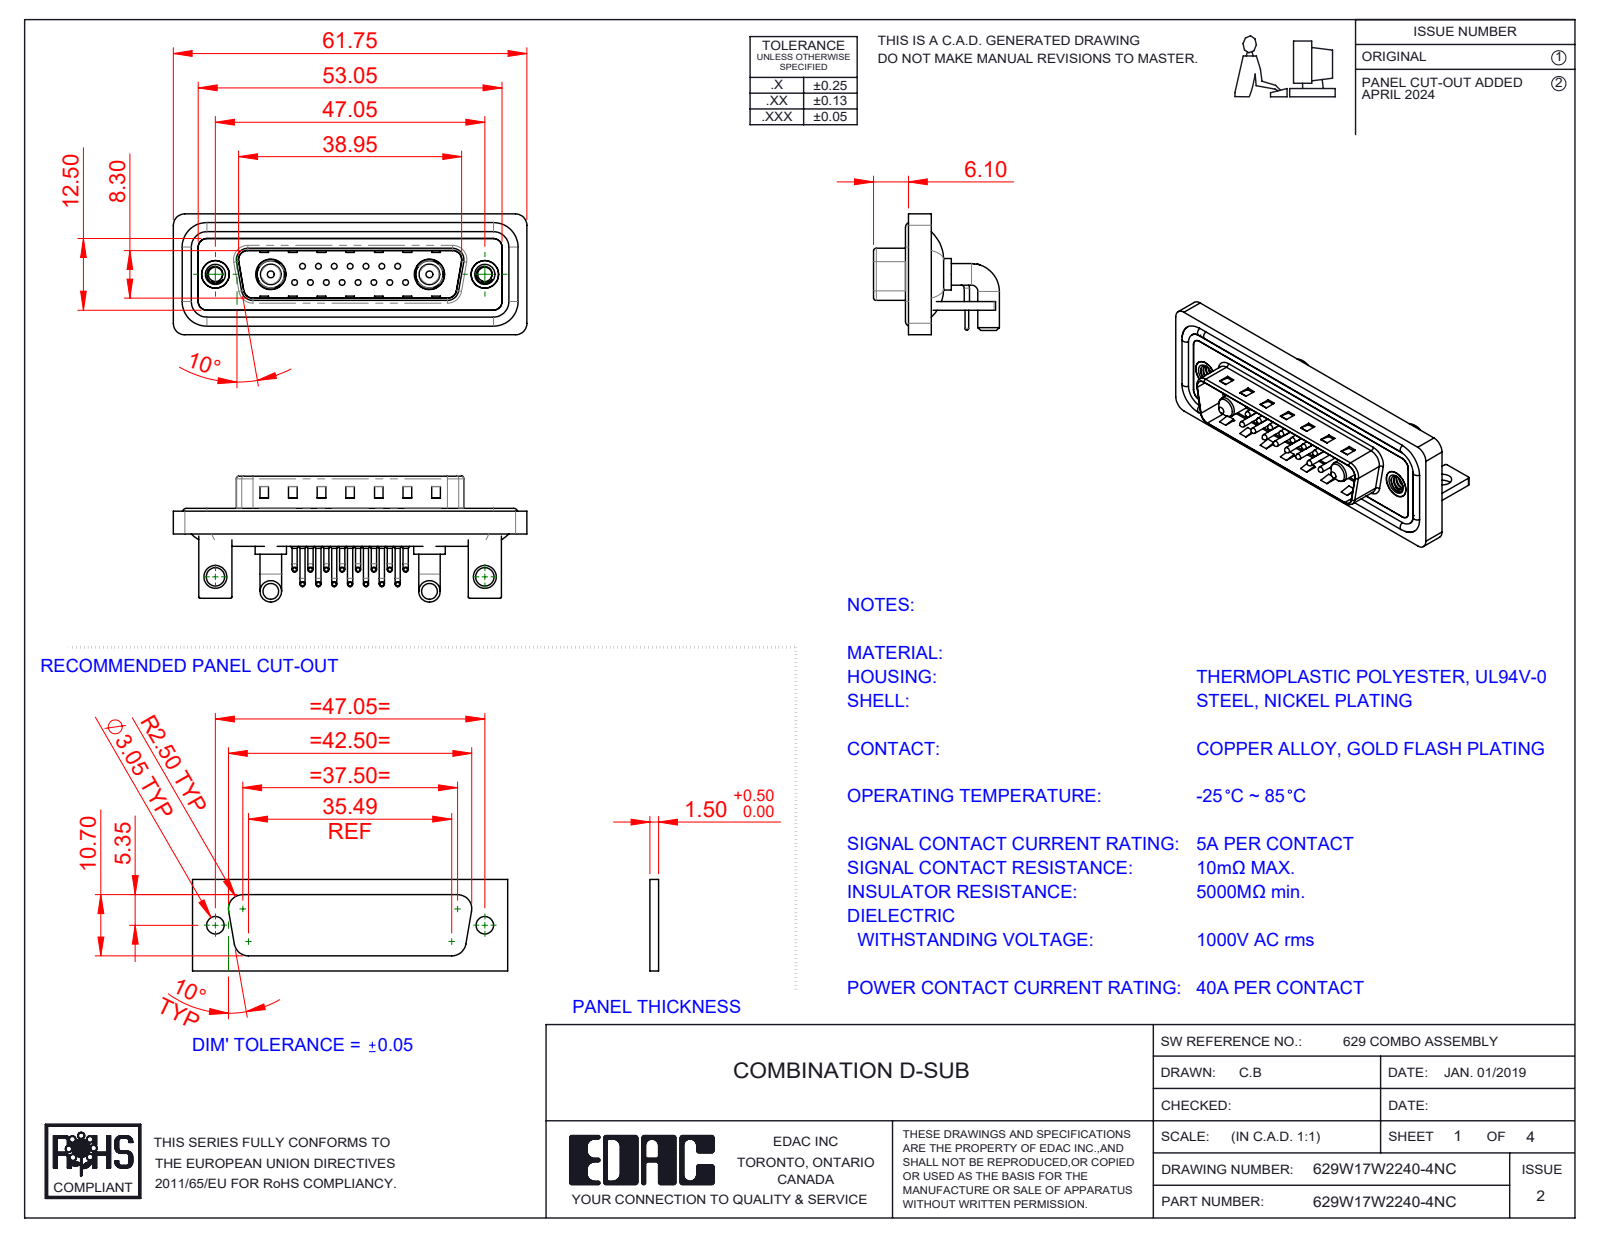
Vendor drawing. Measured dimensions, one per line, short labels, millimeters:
name: 629Combo Waterproof Housing_25 Contacts; 629Combo Threaded Rivet_B; Power Pin_40A RA; 629Combo Contact Row 1 (+6 more)
written by: SolidWorks 2023 (CONFIG_CONTROL_DESIGN)
unit: mm
bodies: 28 solids, 2257 faces (1209 planar, 788 cylindrical, 260 other)
size: 61.75 × 21.98 × 21.1
volume: 7 930 mm³; area: 13 277 mm²
holes: 15× ⌀0.75, 15× ⌀1.6, 15× ⌀2, 2× ⌀2.5, 2× ⌀3.2, 2× ⌀4, 2× ⌀4.8, 2× ⌀4.85, 2× ⌀5, 2× ⌀5.3
bosses: 30× ⌀0.9, 15× ⌀1.5, 15× ⌀1, 15× ⌀0.65, 4× ⌀3.75, 4× ⌀1.6, 2× ⌀5.5, 2× ⌀5.2
rounds: 19× R2, 18× R1.5, 16× R0.25, 15× R1.01, 9× R0.5, 8× R1.6, 4× R0.6, 4× R0.65
face distances: 0.4, 0.8, 2.1, 1.5, 2.9, 1.1, 4.1, 1.6, 4.5, 3.7
hole spacings: 3.16, 2.77, 5.54, 8.31, 5.04, 7.49, 11.08, 5.03
